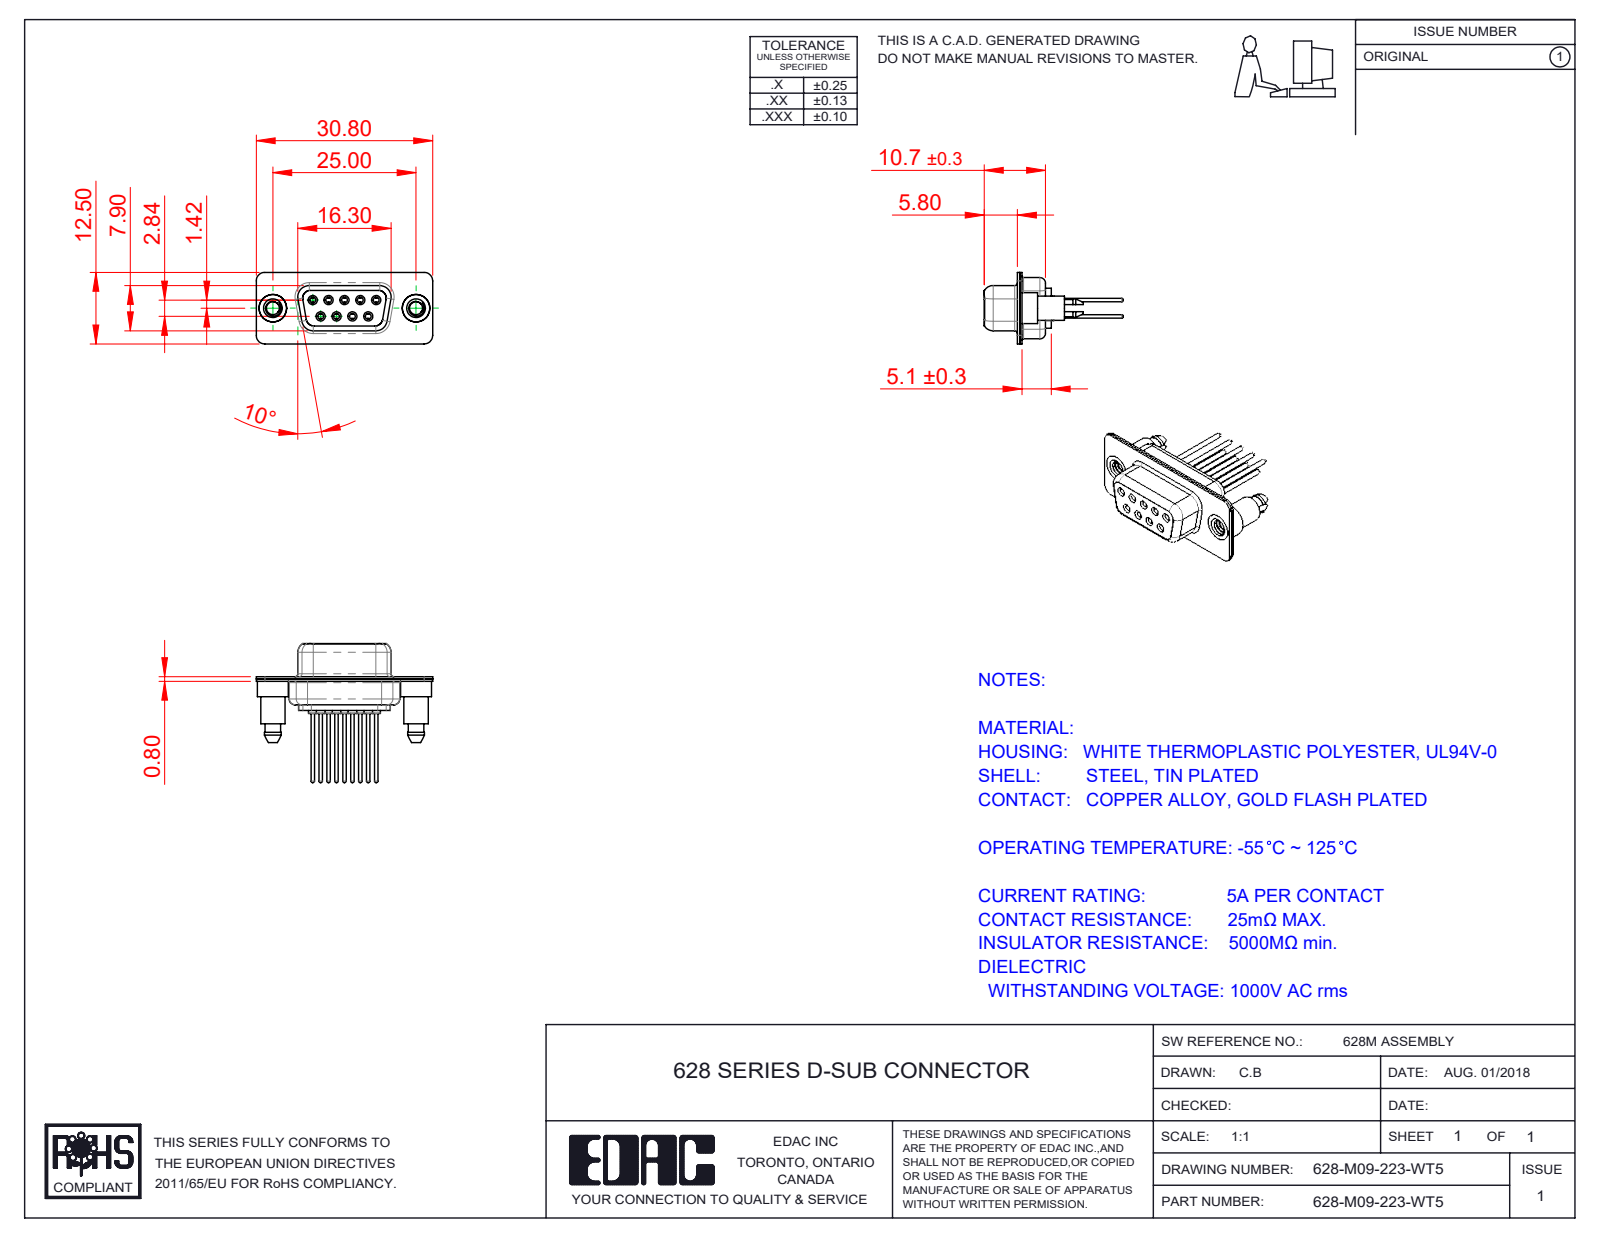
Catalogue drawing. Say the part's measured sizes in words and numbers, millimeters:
The part is named "628M Contact Row 2_23; 628-M09-223-WT5; 628M Shell Rear_09 Contacts; 628M Contact Row 1_23 (+3 more)". Its 3-D file was written by "SolidWorks 2020 (CONFIG_CONTROL_DESIGN)". It is 14 solids with 824 faces: 218 planar, 340 cylindrical and 266 other. Overall it measures 30.8 by 24.27 by 12.5 millimeters. Its volume is 1 853 cubic millimeters and its surface area 4 869 square millimeters. Round holes: 9 of diameter 1, 9 of diameter 1.1, 9 of diameter 1.7, 9 of diameter 1.8, 9 of diameter 2, 2 of diameter 2.26, 2 of diameter 4, 2 of diameter 4.8. Round bosses or shafts: 9 of diameter 2.2, 9 of diameter 1.6, 9 of diameter 1.5, 9 of diameter 0.6, 2 of diameter 5.4, 2 of diameter 4.9, 2 of diameter 4.25. Partial cylindrical surfaces (rounded edges, fillets, slot ends): 18 of radius 1.5, 12 of radius 2, 10 of radius 1.6, 8 of radius 1.35, 4 of radius 0.25, 4 of radius 0.5, 4 of radius 0.6, 4 of radius 0.65. The main face-to-face distances are 0.4, 1.4, 0.45, 8.45, 0.8, 1.8, 1, 8.9, 6.2, 7.05. The hole center spacings are 3.16, 2.77, 5.54, 5.03, 5.04, 8.31, 7.1, 7.48.
